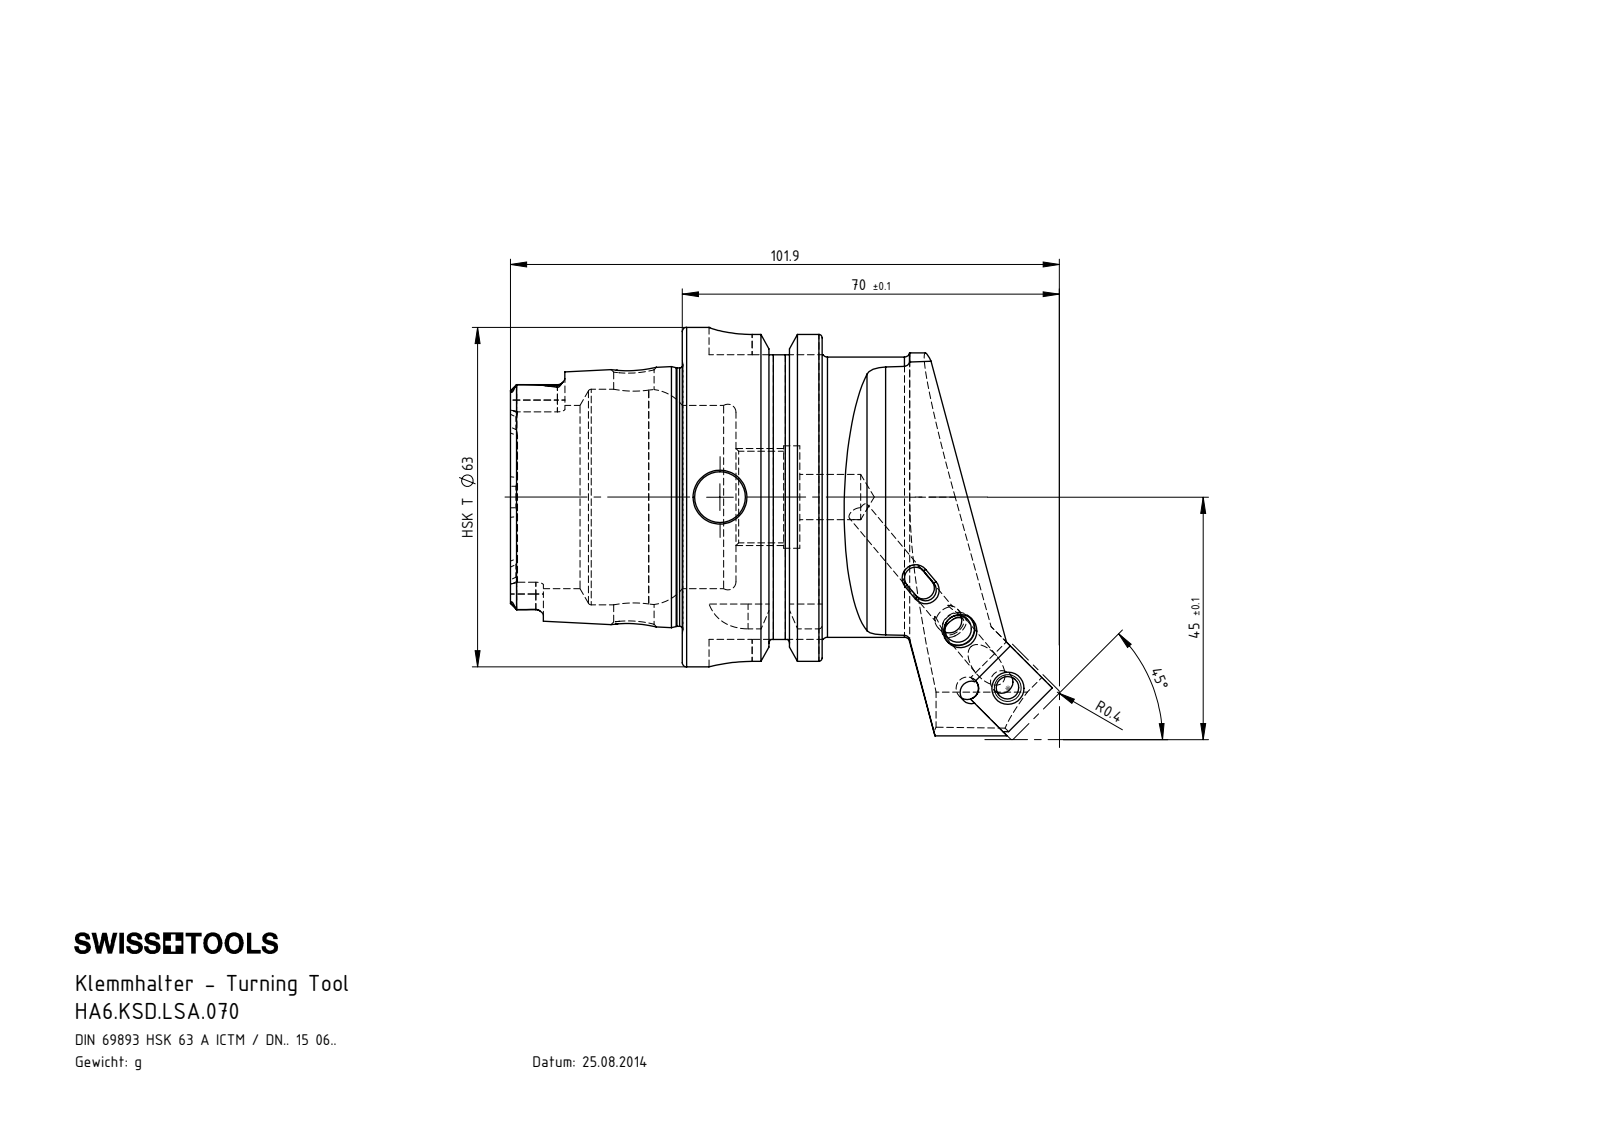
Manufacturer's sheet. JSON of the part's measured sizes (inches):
{"part_name": "KVT_MB_600_060; HA6.KSD.LSA.070; SNMG120404; WSD-ER2.101.003_A (+6 more)", "step_written_by": "SolidWorks 2022 (CONFIG_CONTROL_DESIGN)", "units": "inches", "bodies": {"solids": 10, "faces": 485, "planar": 126, "cylindrical": 156, "other": 203}, "overall_size": [4.012, 3.012, 2.48], "volume_in3": 8.211, "surface_area_in2": 54.1, "round_holes": [[0.079, 3], [0.197, 3], [0.165, 2], [0.244, 2], [0.315, 2], [0.094, 1], [0.118, 1], [0.203, 1], [0.236, 1], [0.256, 1], [0.276, 1], [0.295, 1]], "round_bosses_or_shafts": [[0.236, 2], [0.118, 2], [2.48, 1], [2.163, 1], [2.047, 1], [1.887, 1], [0.551, 1], [0.453, 1]], "partial_cylinders_radius": [[0.015, 6], [0.027, 6], [0.055, 6], [0.016, 4], [0.113, 4], [0.315, 4], [0.031, 3], [0.059, 3]], "face_to_face_distances": [1.022, 0.63, 0.392, 1.256, 1.648, 2.278, 2.079, 0.858, 0.467, 2.114], "hole_center_spacings": [0.315, 0.591, 0.906, 0.298, 0.323, 0.41, 0.583, 0.315]}
